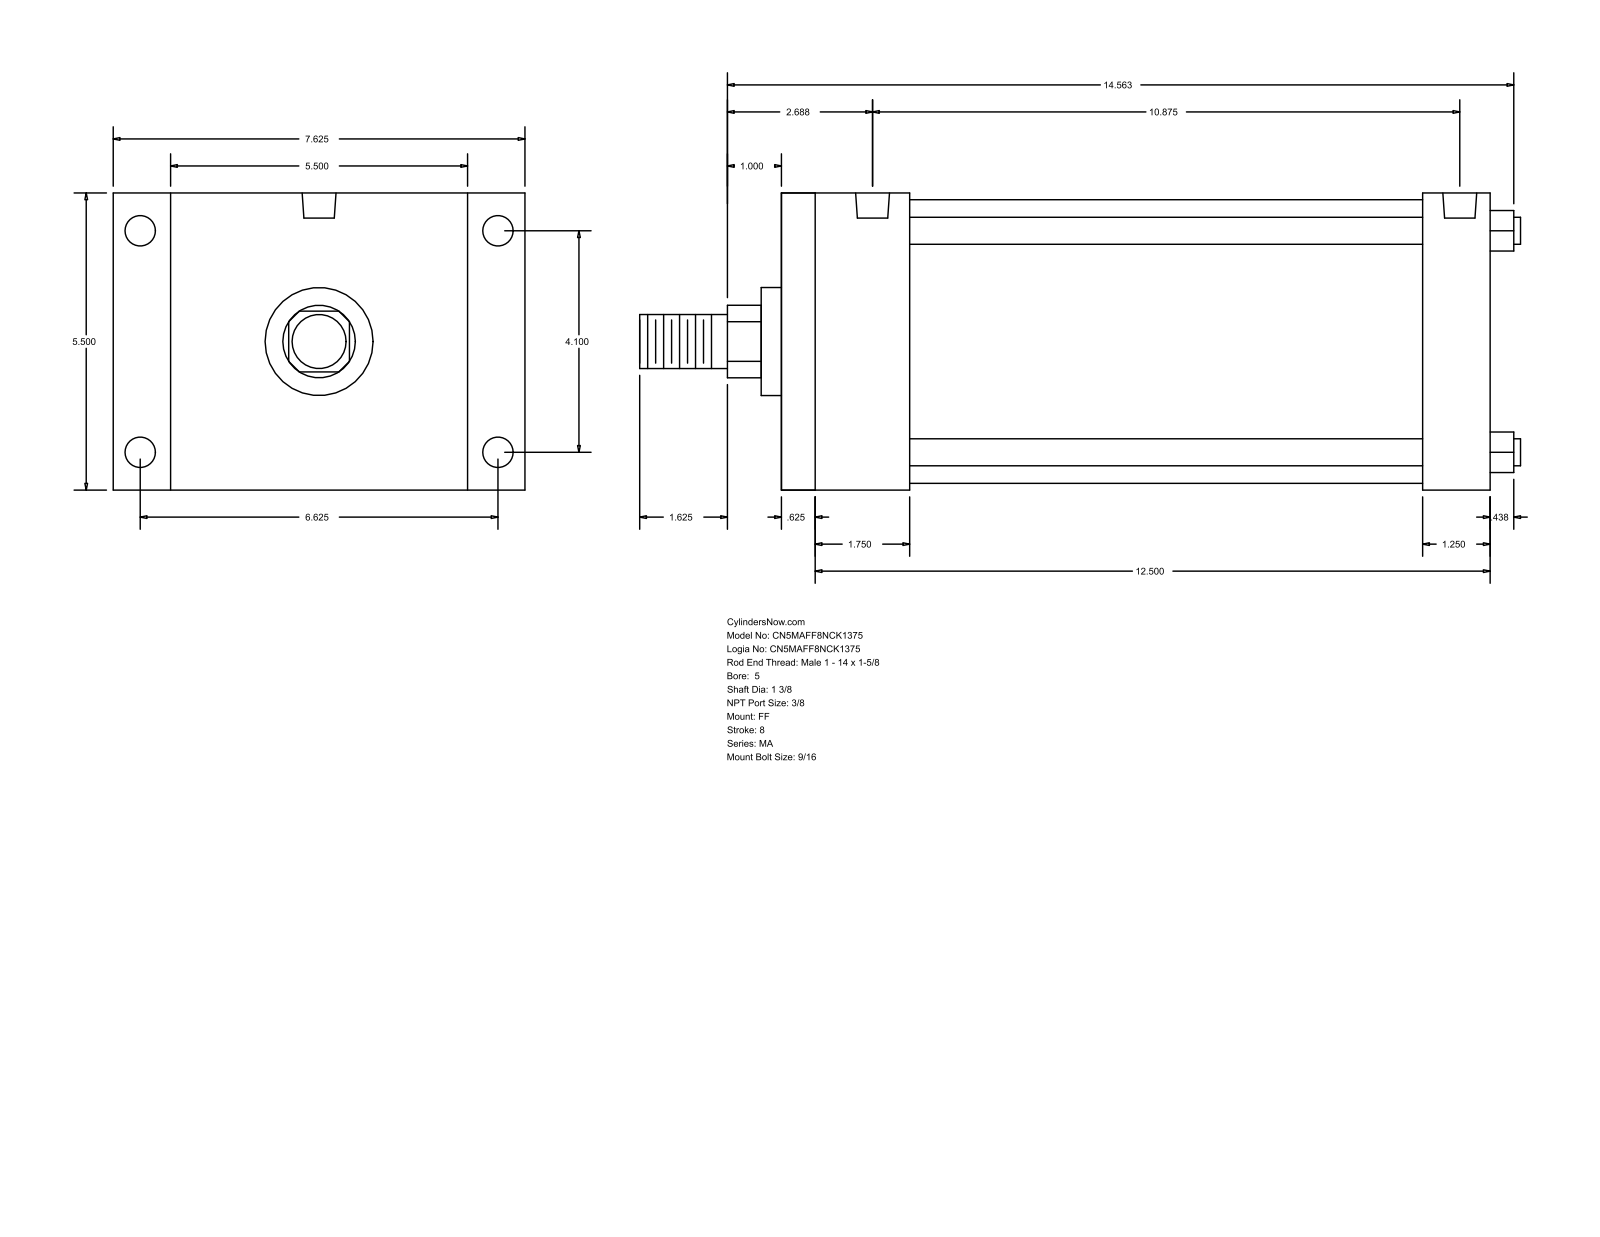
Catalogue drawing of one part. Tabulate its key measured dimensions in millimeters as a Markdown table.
| quantity | value |
| --- | --- |
| part name | MA_FF__0500_1.375 |
| STEP written by | GSSL Pune (CONFIG_CONTROL_DESIGN) |
| units | millimeters |
| bodies | 0 solids, 92 faces (64 planar, 28 cylindrical, 0 other) |
| overall size | 414.34 × 193.68 × 139.7 |
| round holes (diameter × count) | 11.11 × 4, 14.29 × 4, 15.93 × 2 |
| round bosses / shafts (diameter × count) | 12.7 × 4, 133.35 × 1, 50.8 × 1, 34.92 × 1, 25.4 × 1 |
| partial cylindrical surfaces (radius × count) | 17.06 × 1 |
| main face-to-face distances | 139.7, 333.37, 15.87, 317.5, 301.62, 285.75, 31.75, 60.32, 44.45, 241.3 |
| hole center spacings | 104.14, 168.28, 197.9, 266.7, 4.76, 4.77, 271.46, 271.47 |
